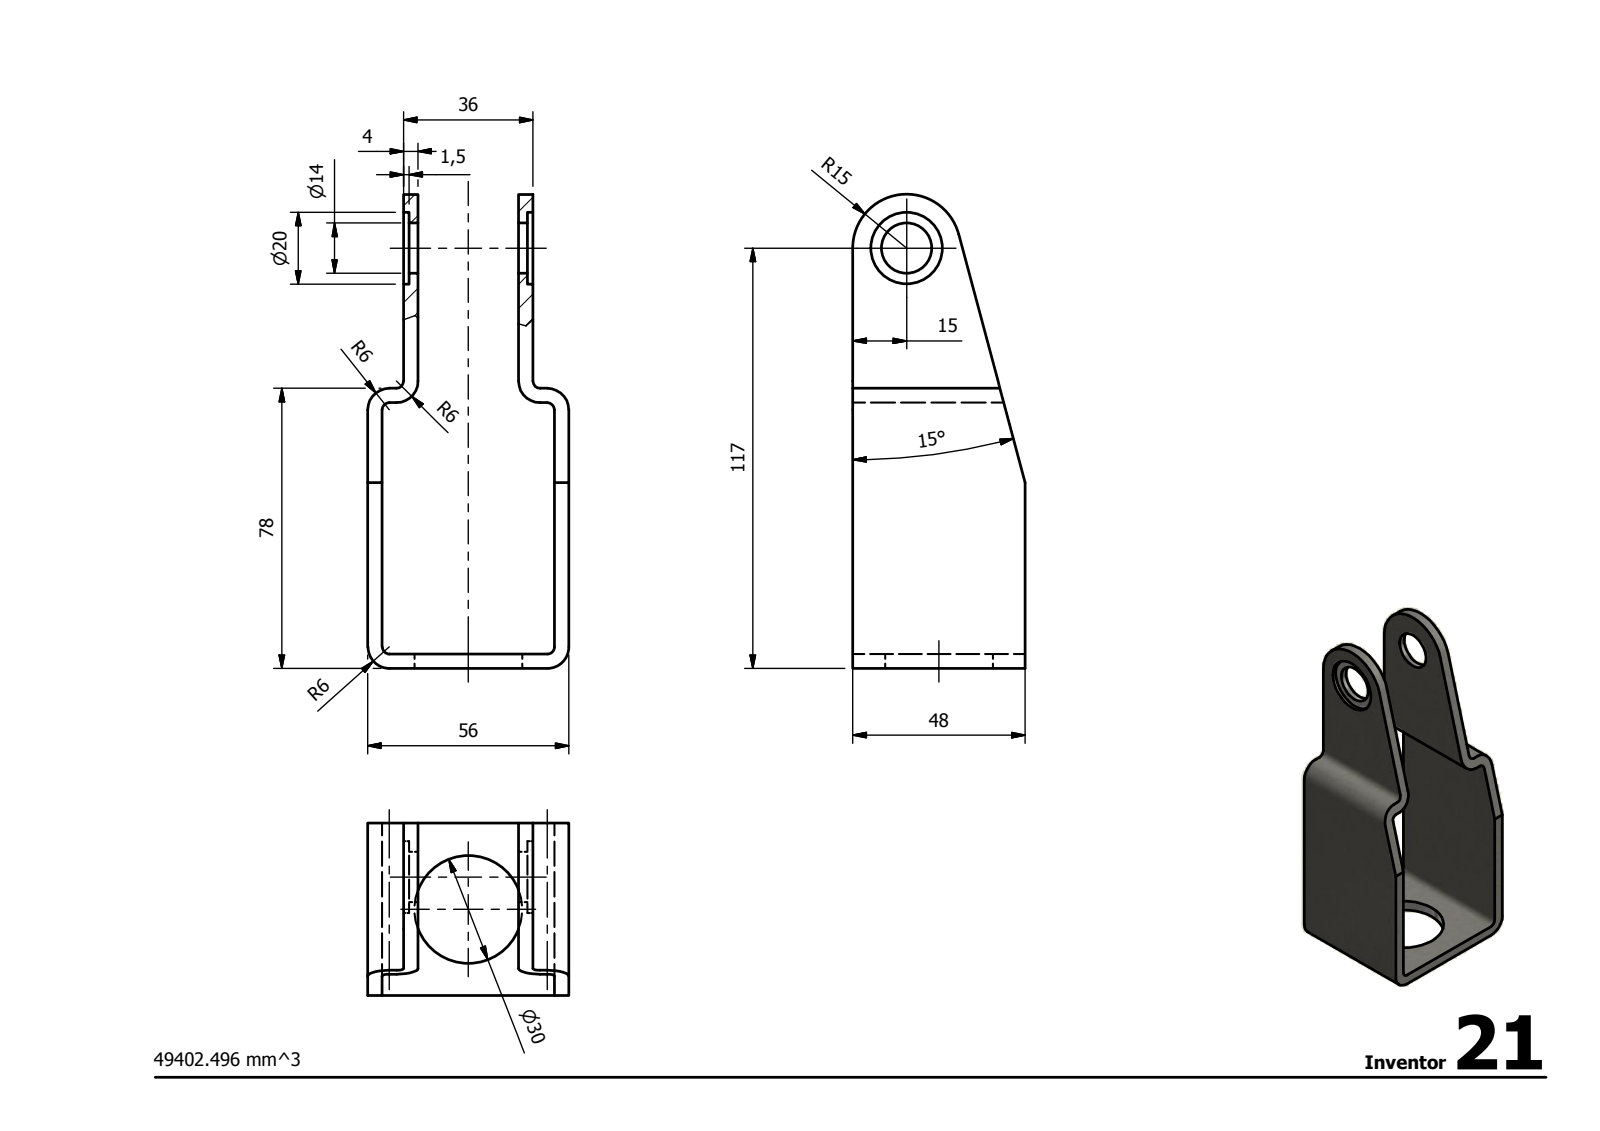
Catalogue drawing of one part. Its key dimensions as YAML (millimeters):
step_written_by: "Autodesk Inventor 2014 (AUTOMOTIVE_DESIGN)"
units: millimeters
bodies: {solids: 1, faces: 39, planar: 20, cylindrical: 19, other: 0}
overall_size: [132, 56, 48]
volume: 49402
surface_area: 28458
round_holes:
  - {diameter: 14, count: 1}
  - {diameter: 20, count: 1}
  - {diameter: 30, count: 1}
partial_cylinders:
  - {radius: 2, count: 6}
  - {radius: 6, count: 6}
  - {radius: 15, count: 1}
face_to_face_distances: [4, 52, 10, 42, 48, 56, 14, 38, 46, 6]
